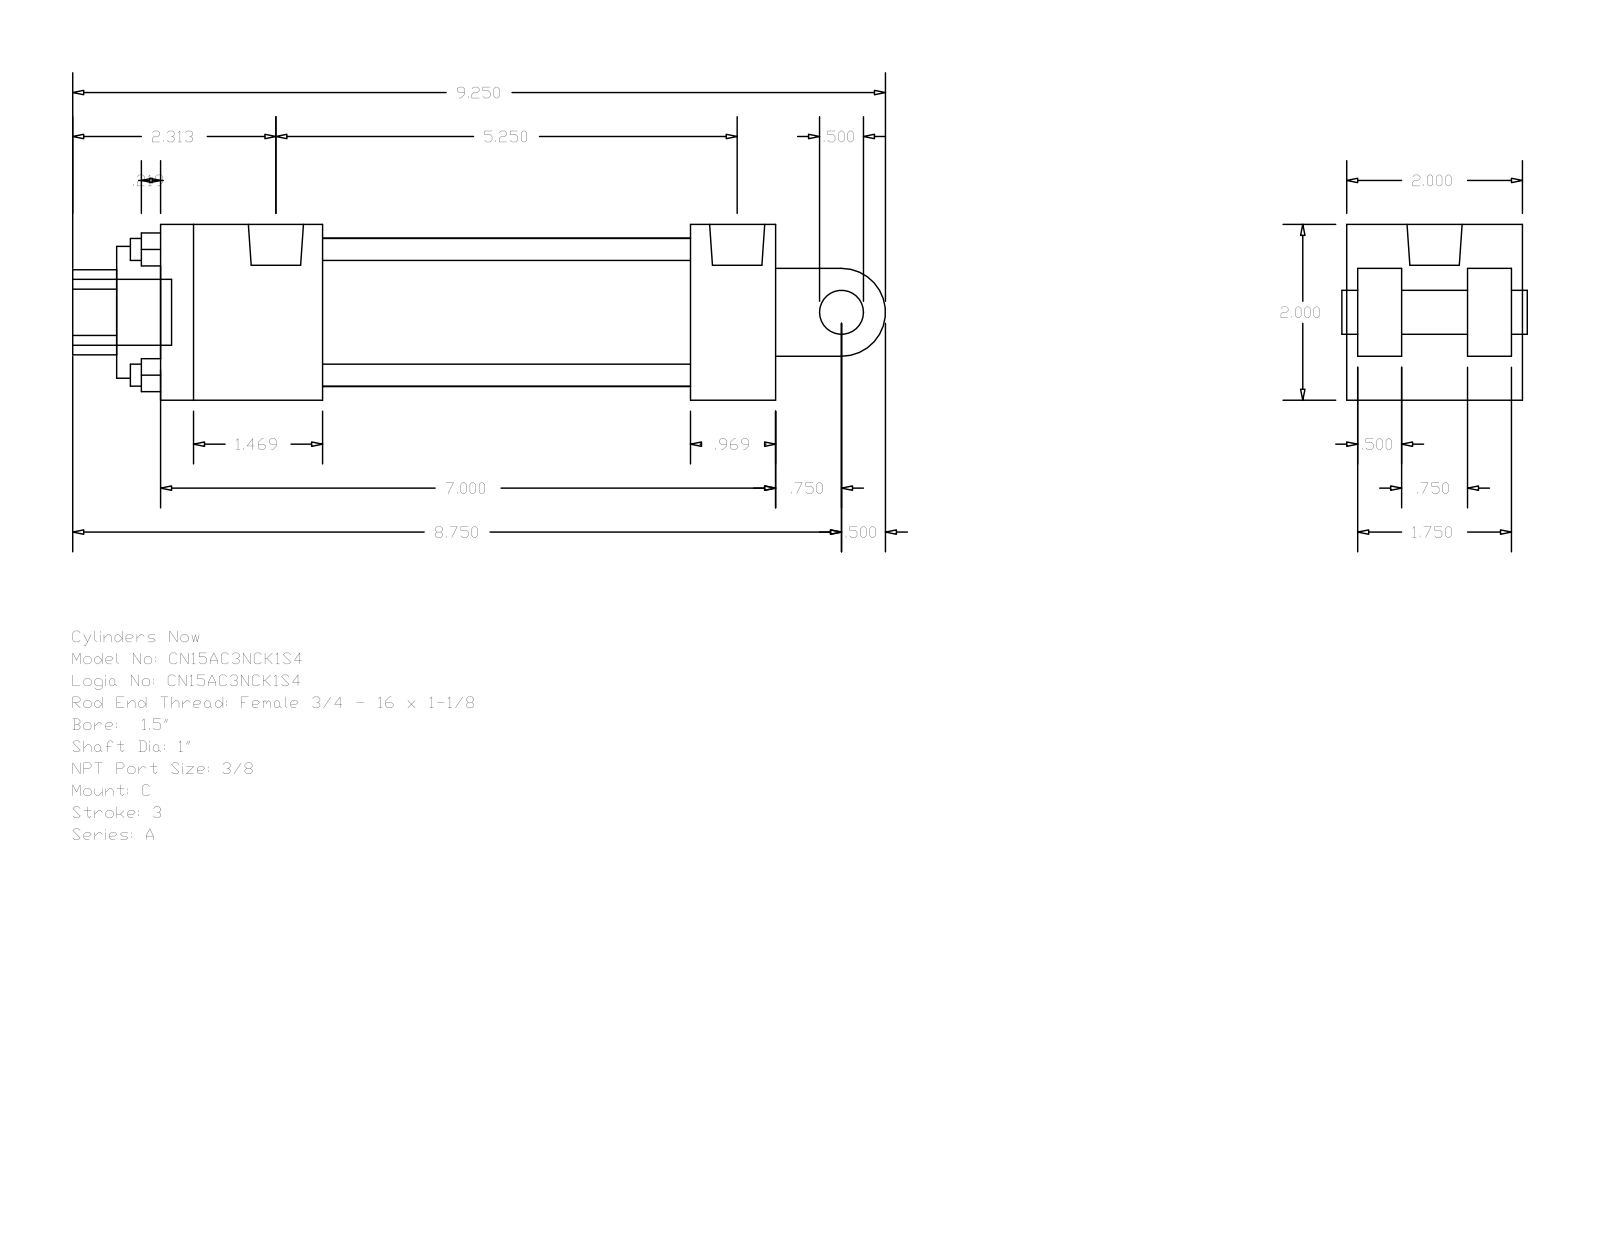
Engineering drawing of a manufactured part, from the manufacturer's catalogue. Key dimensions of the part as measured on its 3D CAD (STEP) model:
Part name (STEP PRODUCT): A_C__0150_1
STEP written by: GSSL Pune (CONFIG_CONTROL_DESIGN)
Units: millimetres
Bodies: 0 solids, 99 faces (70 planar, 29 cylindrical, 0 other)
Overall size (bounding box): 234.95 × 50.8 × 50.8
Round holes (diameter × count): ⌀6.35 ×4, ⌀5.56 ×2, ⌀15.93 ×1, ⌀25.4 ×1, ⌀38.1 ×1, ⌀42.93 ×1
Round bosses / shafts (diameter × count): ⌀5.56 ×2, ⌀19.05 ×1, ⌀15.93 ×1, ⌀12.7 ×1
Partial cylindrical surfaces — rounded edges, fillets, slot ends (radius × count): R12.29 ×1, R12.7 ×1
Main face-to-face distances: 50.8, 12.7, 3.17, 15.87, 47.63, 34.93, 31.76, 177.8, 153.19, 24.61
Hole centre spacings: 25.68, 36.32, 51.36, 3.97
